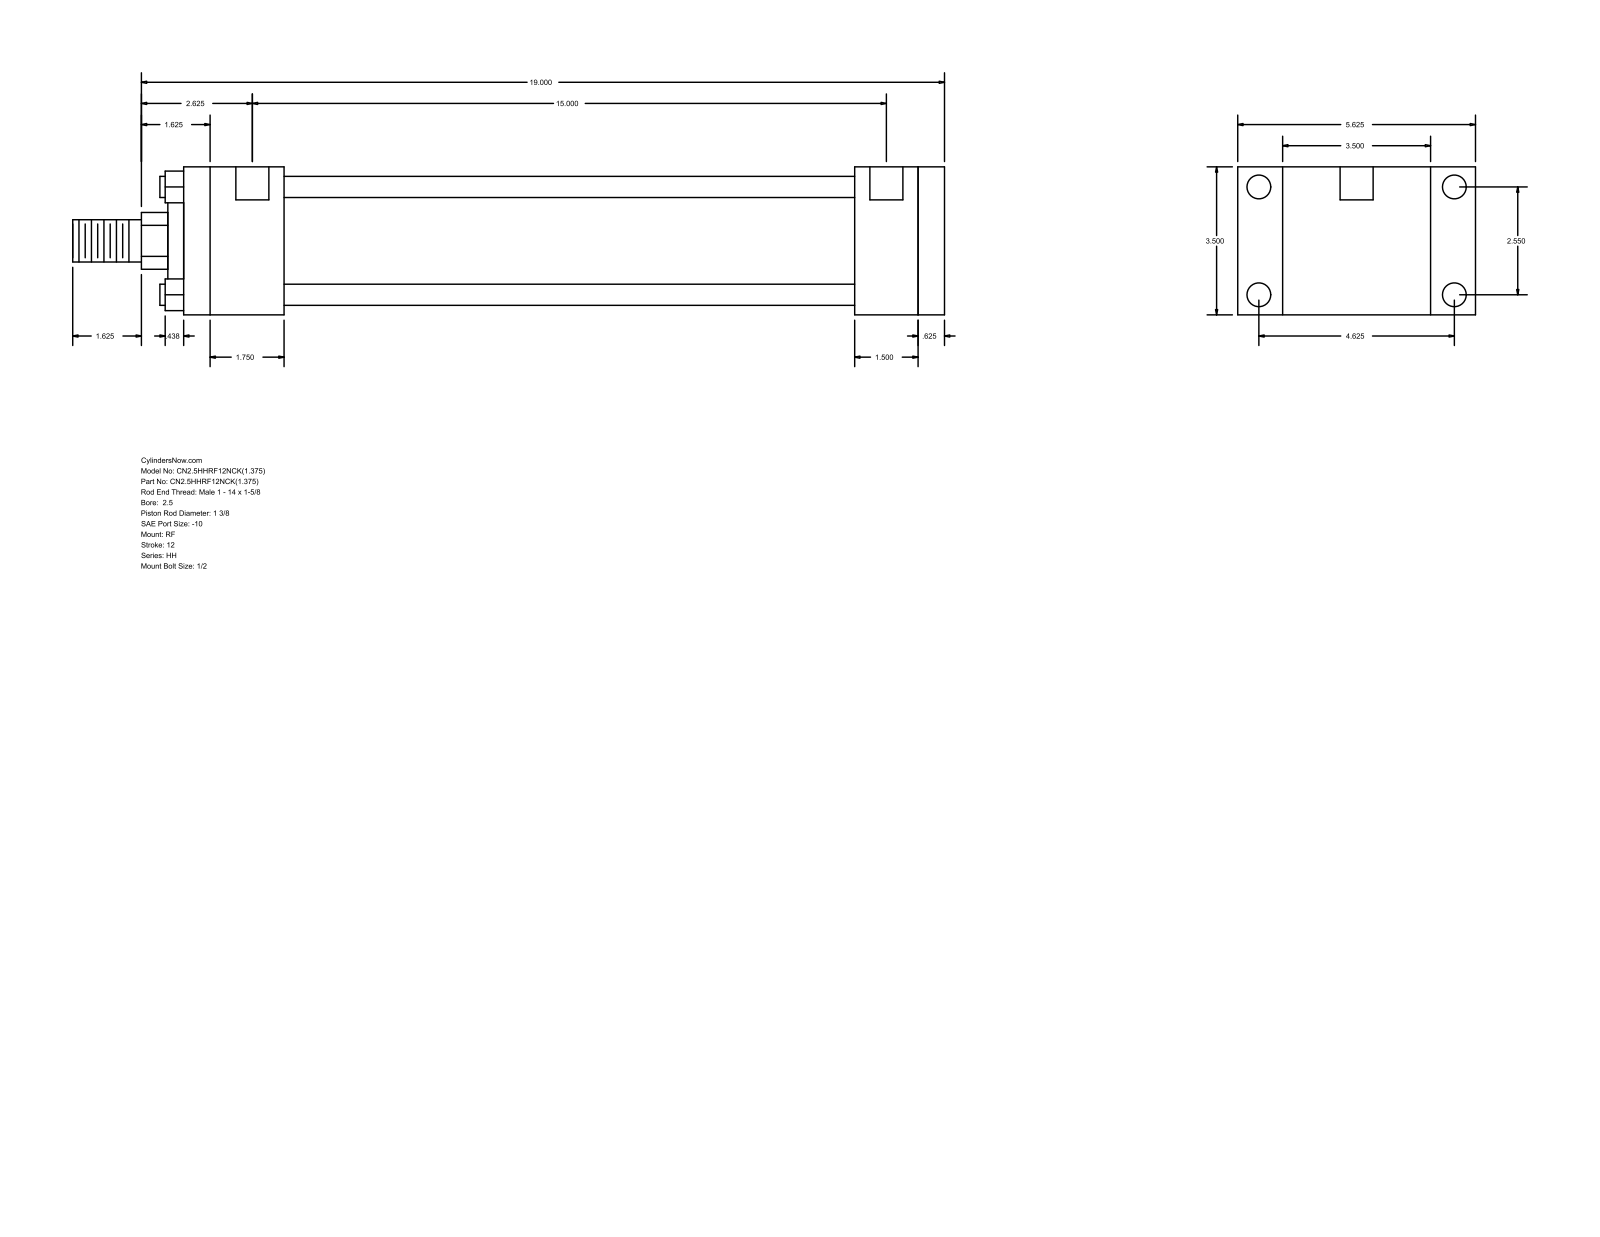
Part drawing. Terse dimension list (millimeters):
name: HH_RF__0250_1.375
written by: GSSL Pune (CONFIG_CONTROL_DESIGN)
unit: mm
bodies: 0 solids, 92 faces (64 planar, 28 cylindrical, 0 other)
size: 523.88 × 142.88 × 88.9
holes: 4× ⌀5.56, 4× ⌀14.3, 2× ⌀19.84
bosses: 4× ⌀12.7, 1× ⌀73.03, 1× ⌀50.8, 1× ⌀34.92, 1× ⌀25.4
rounds: 1× R17.06
face distances: 88.9, 457.2, 441.33, 15.87, 60.32, 381.01, 396.88, 403.22, 342.9, 38.11
hole spacings: 1.58, 64.76, 117.48, 134.15, 382.59, 384.17, 381.01
